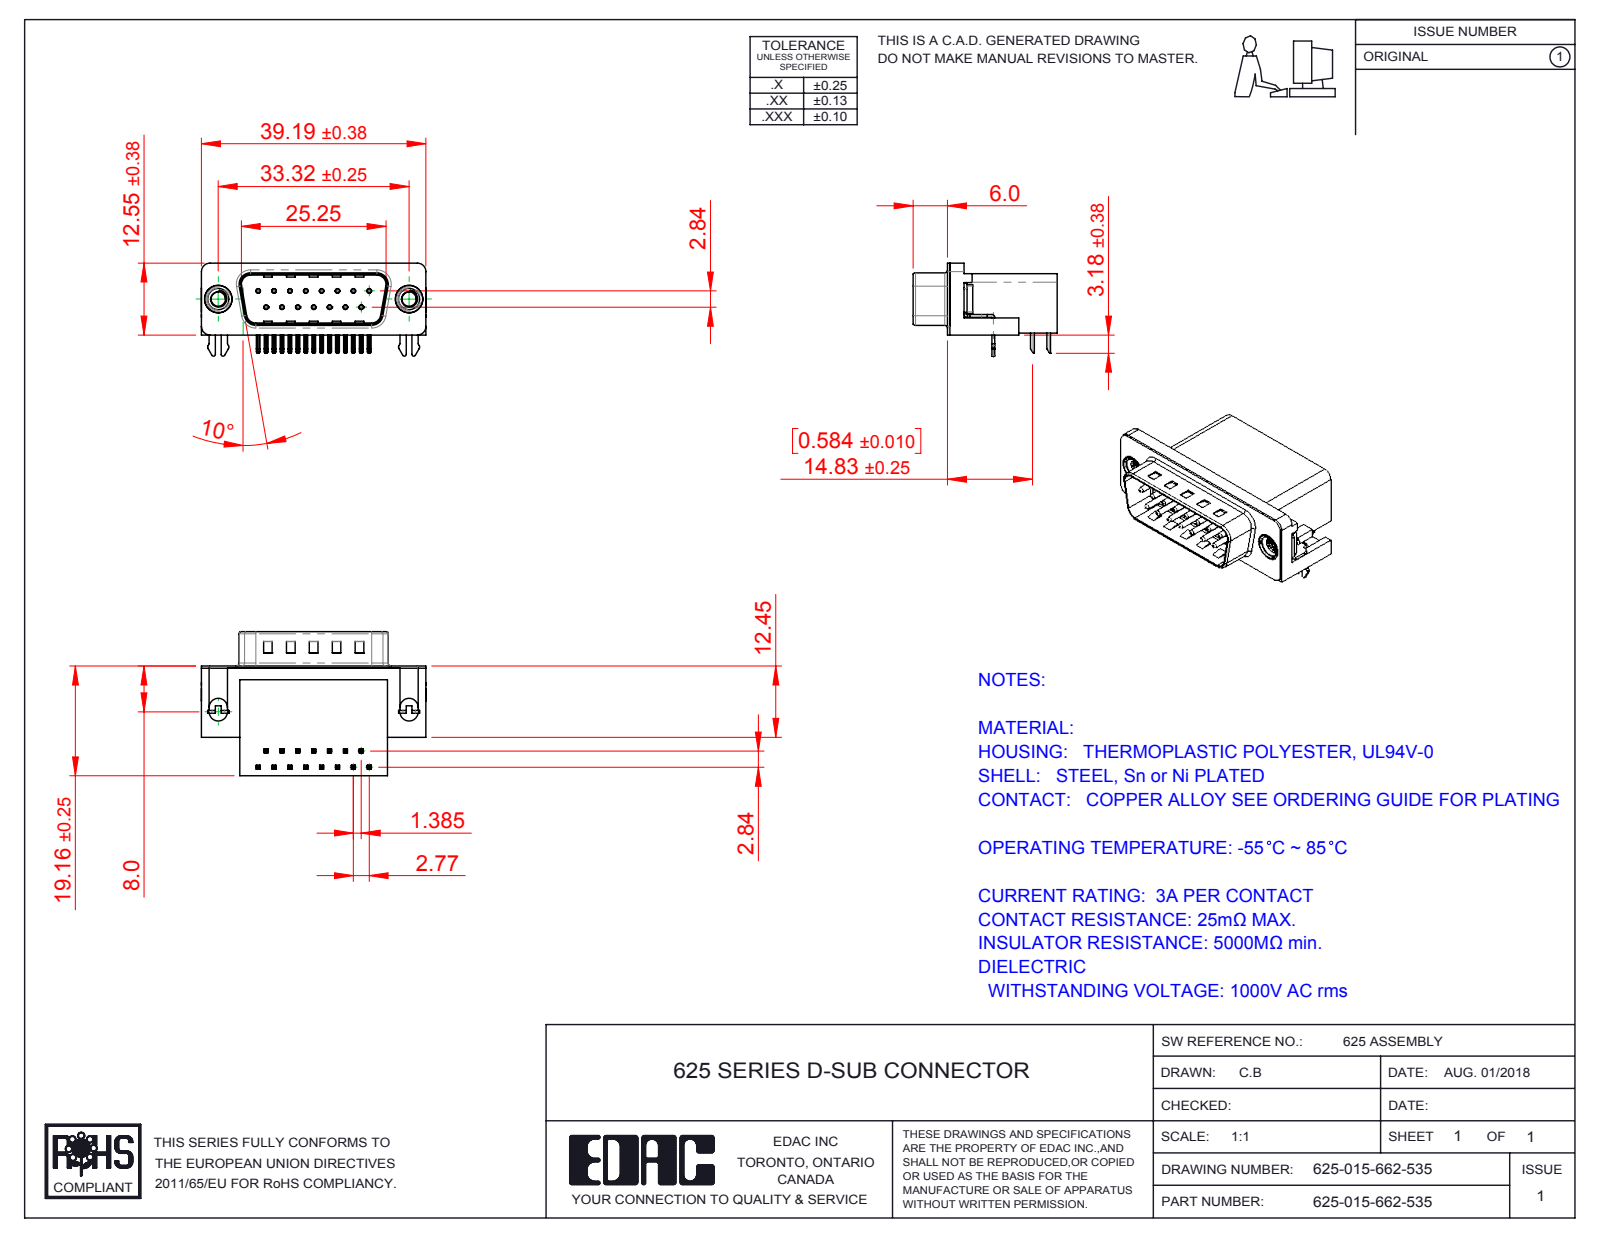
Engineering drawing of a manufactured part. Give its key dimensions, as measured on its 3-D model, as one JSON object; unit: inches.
{"part_name": "625-015-662-535; 625 Shell_15 Socket; 625 M3 Threaded Rivet; 625 2 Prong Board Lock (+3 more)", "step_written_by": "SolidWorks 2016 (CONFIG_CONTROL_DESIGN)", "units": "inches", "bodies": {"solids": 21, "faces": 1519, "planar": 925, "cylindrical": 459, "other": 135}, "overall_size": [1.544, 0.991, 0.64], "volume_in3": 0.381, "surface_area_in2": 9.973, "round_holes": [[0.014, 15], [0.031, 15], [0.098, 2], [0.157, 2], [0.189, 2], [0.197, 2]], "round_bosses_or_shafts": [[0.03, 15], [0.193, 2], [0.187, 2], [0.154, 2]], "partial_cylinders_radius": [[0.01, 68], [0.005, 30], [0.039, 16], [0.02, 14], [0.063, 8], [0.059, 6], [0.013, 4], [0.035, 4]], "face_to_face_distances": [0.016, 0.407, 0.739, 0.083, 0.412, 0.754, 0.067, 0.428, 0.345, 0.64], "hole_center_spacings": [0.124, 0.109, 0.218, 0.327, 0.436, 0.198, 0.198, 0.294]}
